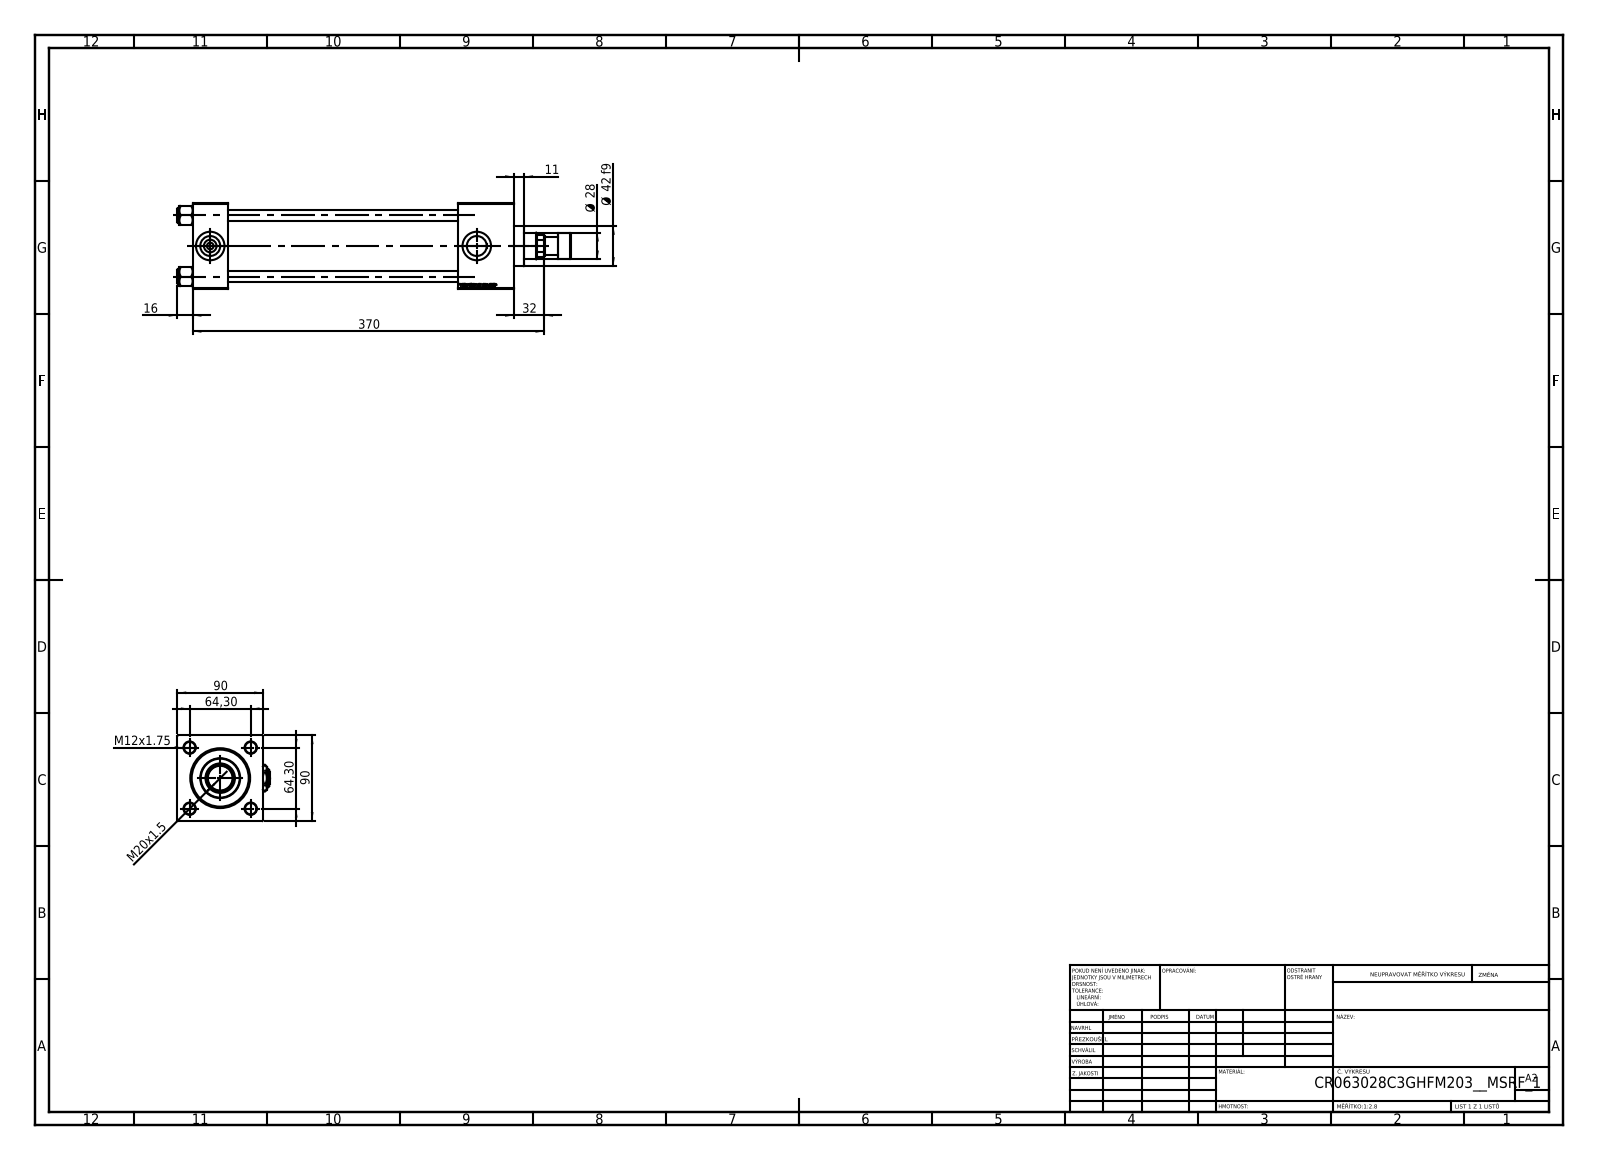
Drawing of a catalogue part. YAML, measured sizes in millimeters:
part_name: "NUT_M5_C; V215CR_C_TYCINKA; Zatka_pro_OIL_PORT; V215CR_VCP_C (+3 more)"
step_written_by: "SolidWorks 2019 (CONFIG_CONTROL_DESIGN)"
units: millimeters
bodies: {solids: 14, faces: 1264, planar: 578, cylindrical: 102, other: 584}
overall_size: [414, 97, 90]
volume: 1261000
surface_area: 306754
round_holes:
  - {diameter: 12, count: 4}
  - {diameter: 7, count: 2}
  - {diameter: 20.96, count: 2}
  - {diameter: 30, count: 2}
  - {diameter: 18.5, count: 1}
  - {diameter: 28, count: 1}
  - {diameter: 31, count: 1}
  - {diameter: 50, count: 1}
  - {diameter: 60, count: 1}
  - {diameter: 63, count: 1}
round_bosses_or_shafts:
  - {diameter: 15, count: 4}
  - {diameter: 69, count: 1}
  - {diameter: 42, count: 1}
  - {diameter: 27, count: 1}
  - {diameter: 18, count: 1}
face_to_face_distances: [90, 37, 301, 338, 59, 279, 242, 309.3, 272.3, 30.3]
hole_center_spacings: [45.47, 64.3, 90.93, 280.5]
